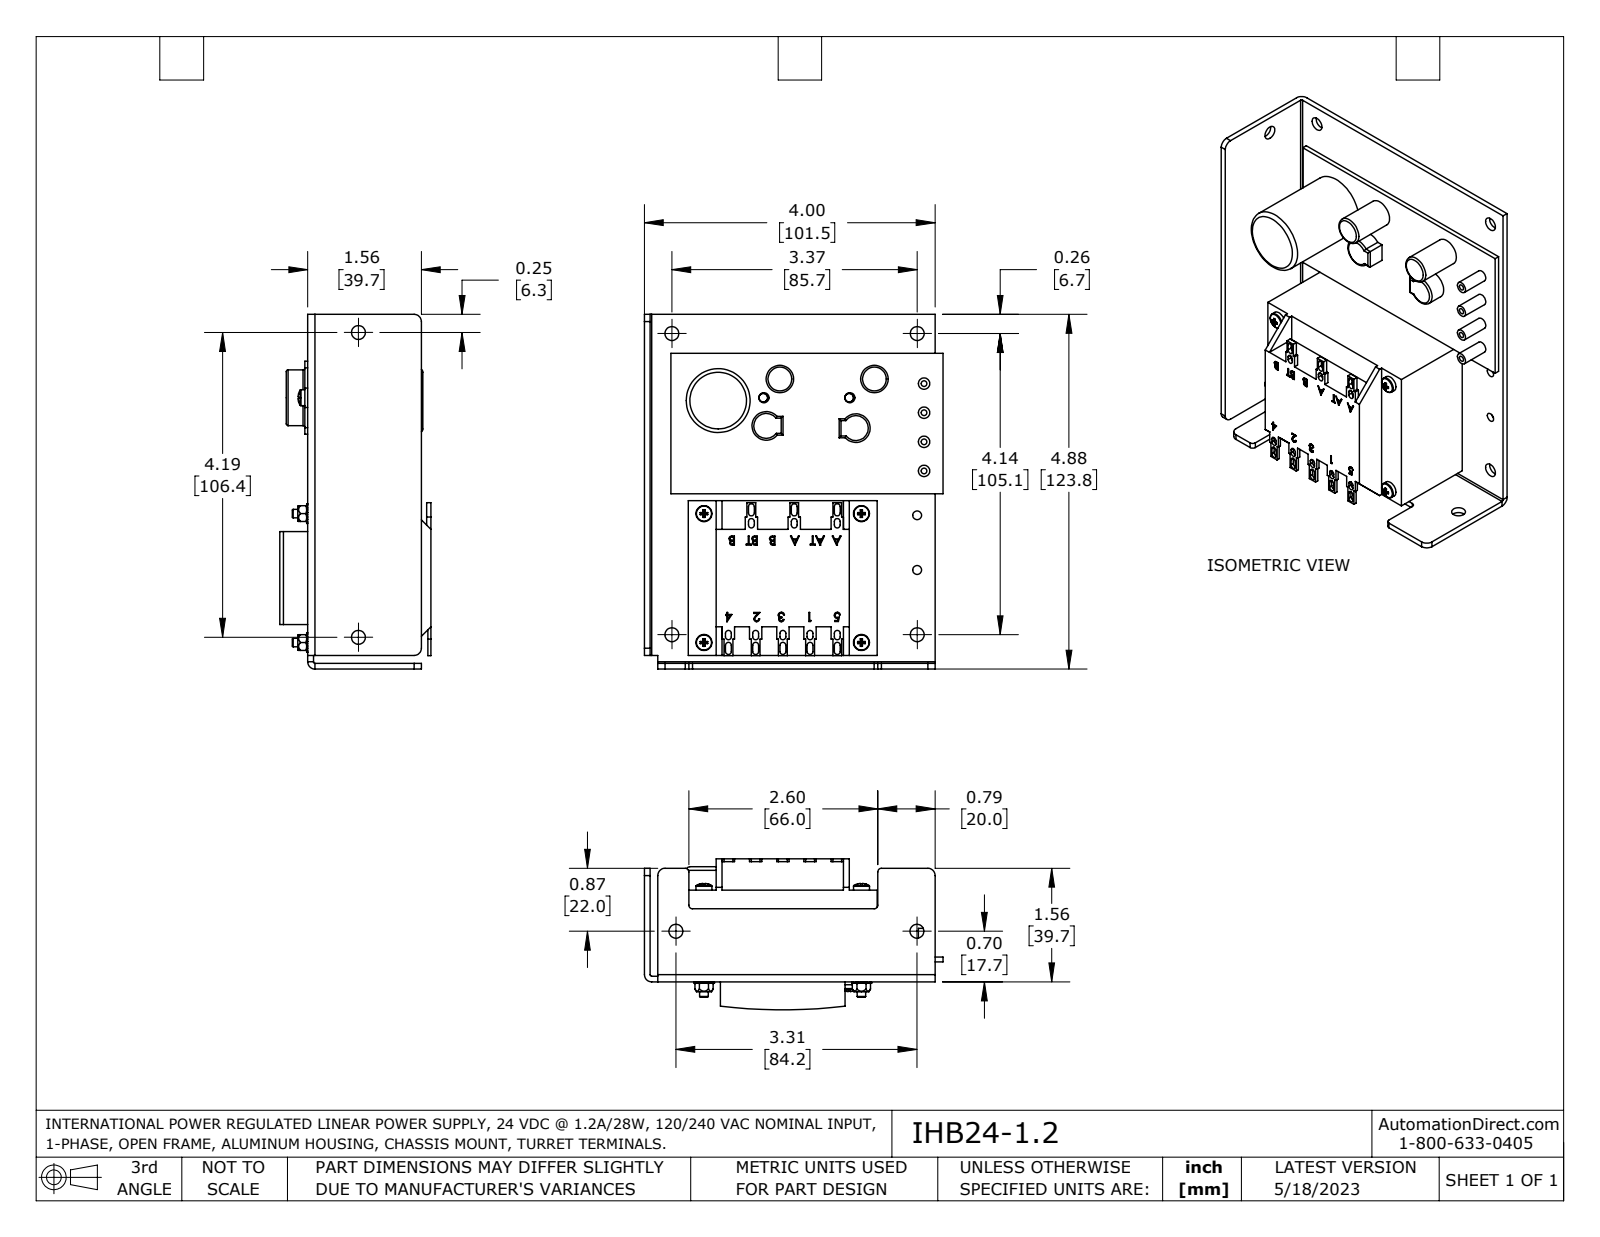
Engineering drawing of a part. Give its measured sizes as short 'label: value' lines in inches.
name: IHB24-1.2
written by: SolidWorks 2021 (AUTOMOTIVE_DESIGN)
unit: in
bodies: 2 solids, 953 faces (634 planar, 213 cylindrical, 106 other)
size: 4.875 × 4.105 × 2.077
volume: 12.44 in³; area: 109.8 in²
holes: 8× ⌀0.191, 6× ⌀0.12, 4× ⌀0.079, 4× ⌀0.13, 2× ⌀0.122, 2× ⌀0.138
bosses: 6× ⌀0.22, 6× ⌀0.118, 4× ⌀0.157, 2× ⌀0.377, 2× ⌀0.25, 1× ⌀0.878, 1× ⌀0.768
rounds: 32× R0.04, 10× R0.1, 6× R0.025, 4× R0.05, 4× R0.1, 4× R0.135, 2× R0.021, 2× R0.162
face distances: 0.079, 0.276, 0.197, 0.343, 0.264, 0.067, 0.078, 2.314, 2.235, 0.188
hole spacings: 0.4, 0.8, 1.181, 1.772, 2.165, 2.798, 3.374, 4.139
